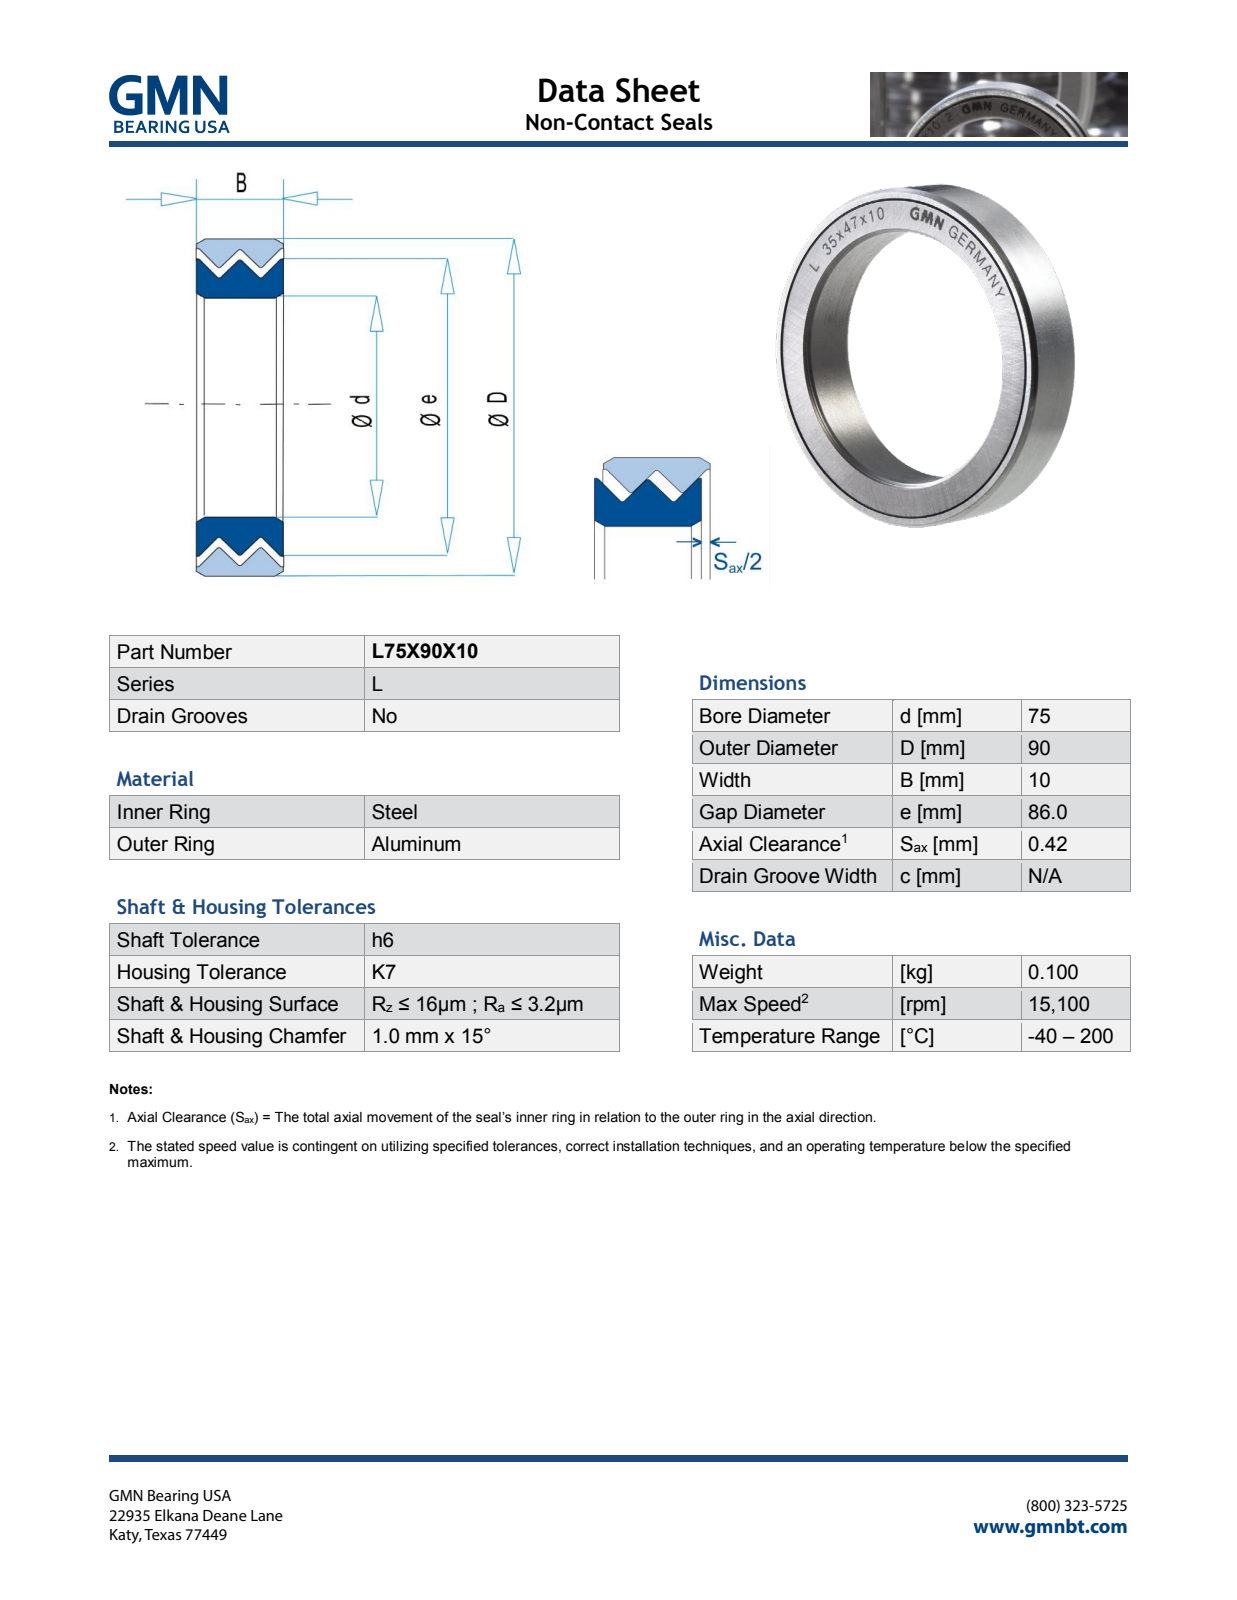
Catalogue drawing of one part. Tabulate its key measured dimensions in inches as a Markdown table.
| quantity | value |
| --- | --- |
| part name | L75X90X10_PRT |
| STEP written by | PRO/ENGINEER BY PARAMETRIC TECHNOLOGY CORPORATION, 2013150 (AUTOMOTIVE_DESIGN) |
| units | inches |
| bodies | 2 solids, 578 faces (522 planar, 12 cylindrical, 44 other) |
| overall size | 3.543 × 3.543 × 0.396 |
| volume | 1.136 in³ |
| surface area | 24.23 in² |
| round holes (diameter × count) | 2.953 × 1, 3.398 × 1 |
| round bosses / shafts (diameter × count) | 3.543 × 1, 3.386 × 1 |
| main face-to-face distances | 0.394, 0.396, 0.015, 0.101, 0.115, 0.012, 0.014, 0.115, 0.013, 0.086 |
